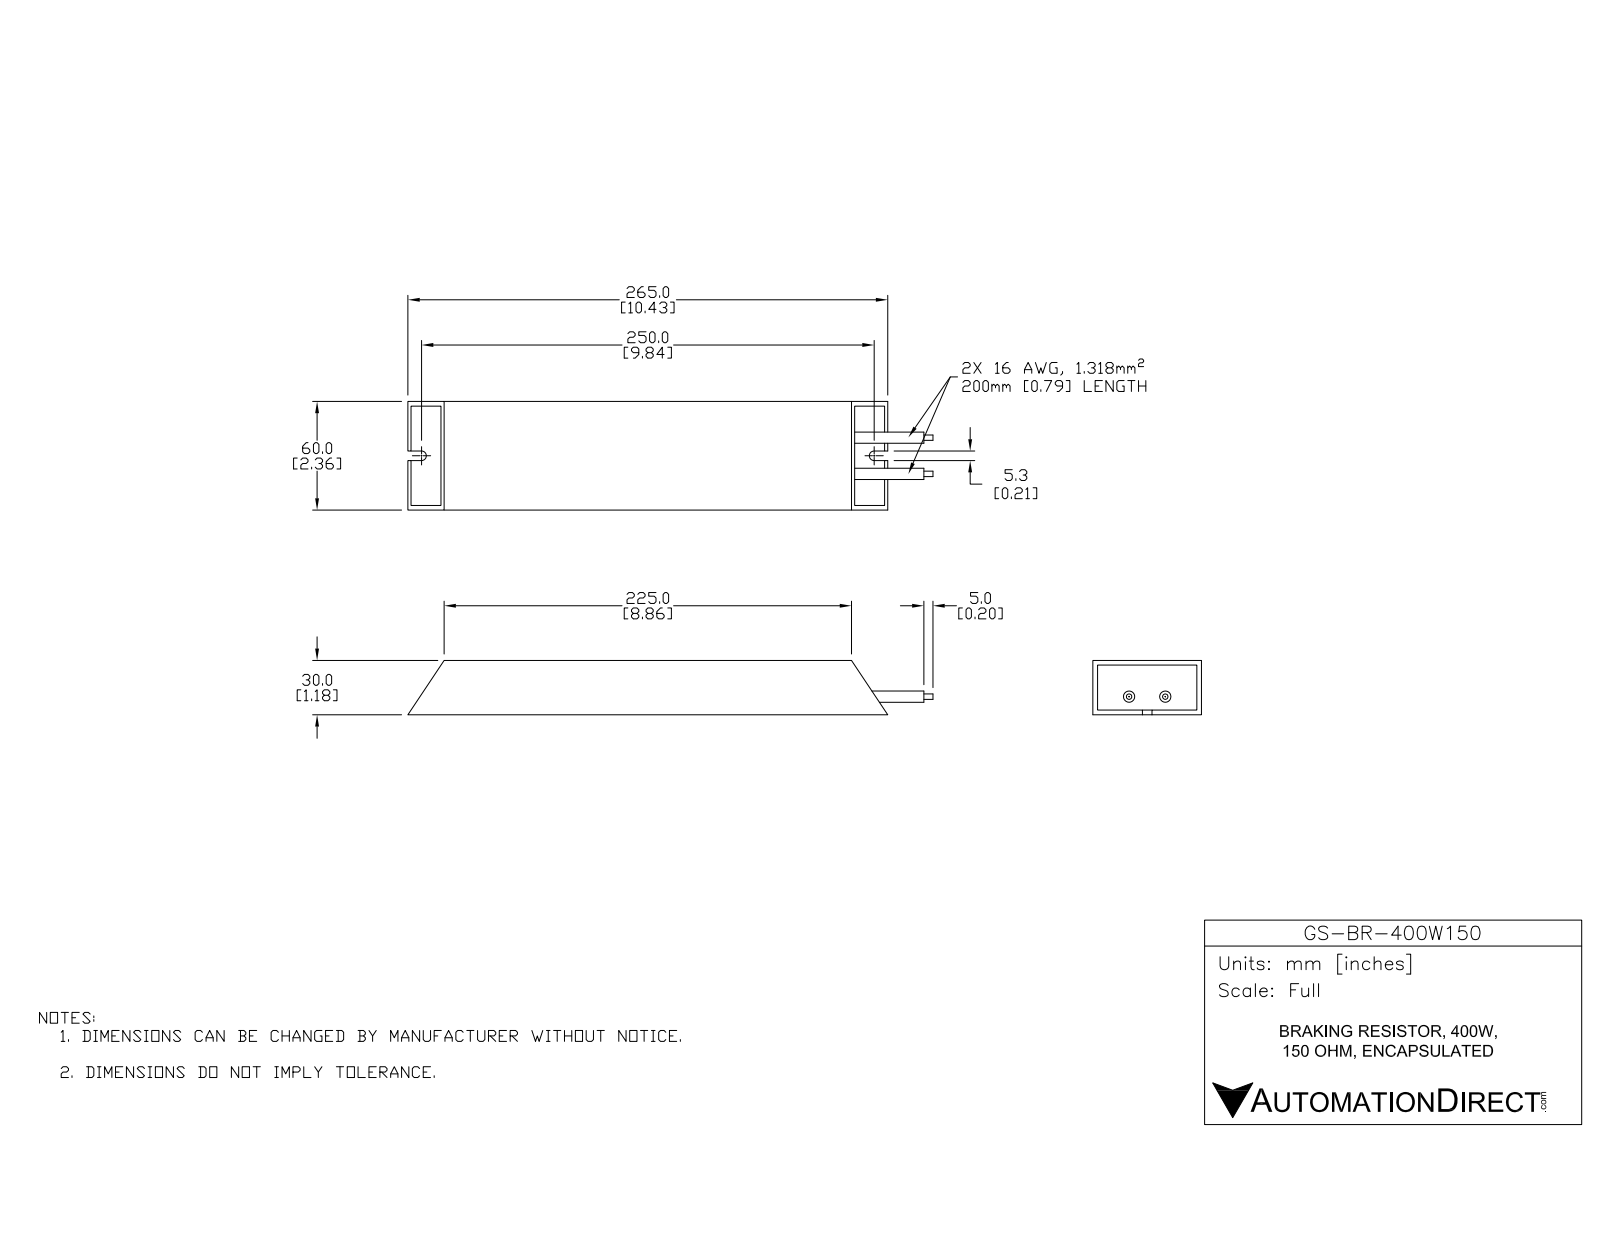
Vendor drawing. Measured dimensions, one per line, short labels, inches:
name: GS-BR-400W150
written by: SolidWorks 2015 (AUTOMOTIVE_DESIGN)
unit: in
bodies: 1 solid, 34 faces (26 planar, 8 cylindrical, 0 other)
size: 11.417 × 2.362 × 1.181
volume: 25.39 in³; area: 81.94 in²
bosses: 2× ⌀0.244, 2× ⌀0.118
rounds: 2× R0.104
face distances: 1.181, 2.362, 0.102, 1.079, 8.858, 2.26, 2.157, 0.976, 1.575, 1.472
